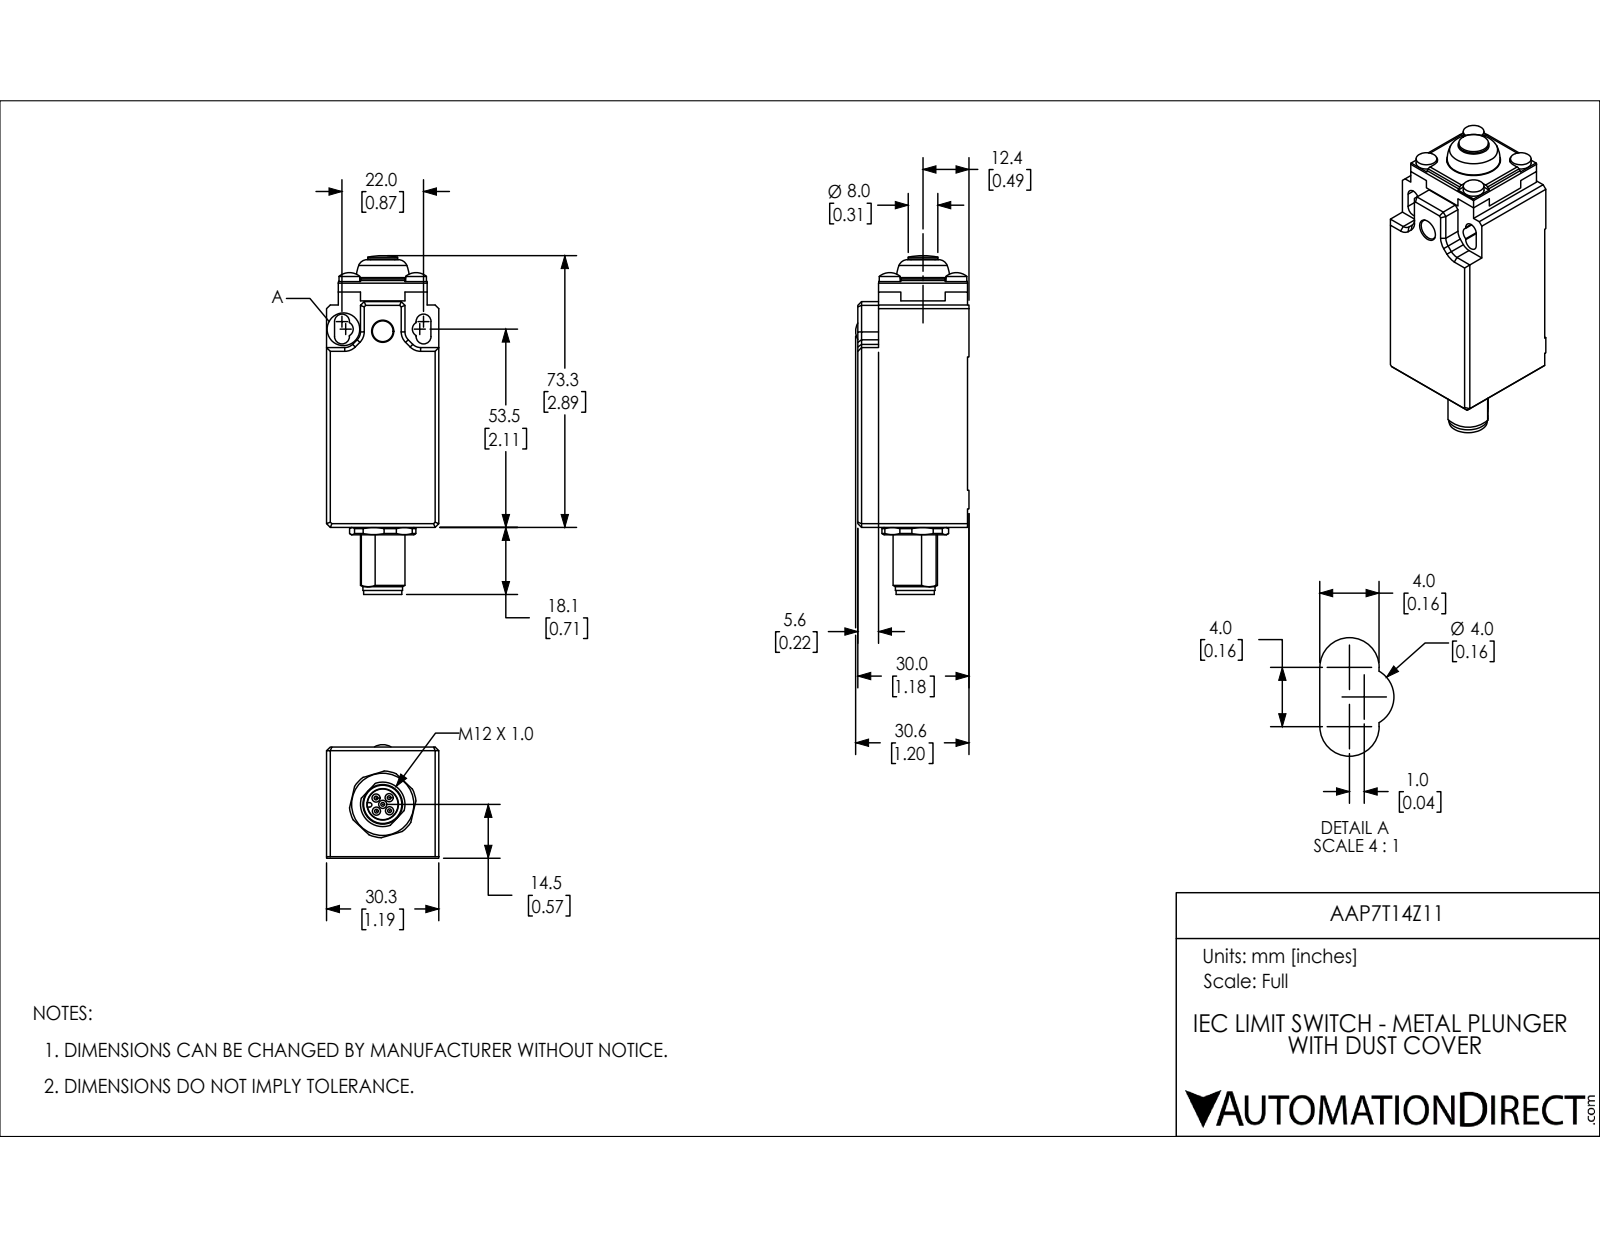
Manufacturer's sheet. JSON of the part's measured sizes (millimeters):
{"part_name": "AAP7T14Z11", "step_written_by": "SolidWorks 2018 (AUTOMOTIVE_DESIGN)", "units": "millimeters", "bodies": {"solids": 5, "faces": 314, "planar": 139, "cylindrical": 120, "other": 55}, "overall_size": [91.4, 30.6, 30.3], "volume_mm3": 58800, "surface_area_mm2": 15700, "round_holes": [[2.2, 5], [6, 1], [8.1, 1], [13, 1], [14, 1], [14.5, 1], [16, 1]], "round_bosses_or_shafts": [[5.6, 5], [1.4, 5], [1, 5], [14.3, 1], [10.7, 1], [10.3, 1], [8, 1], [6.5, 1]], "partial_cylinders_radius": [[1, 8], [3, 8], [2, 6], [0.6, 1], [6, 1], [9, 1], [10, 1], [10.2, 1]], "face_to_face_distances": [30.3, 29.6, 61.1, 0.4, 30, 6, 24, 1, 1.1, 66.2], "hole_center_spacings": [2.5, 3.5, 1.8, 1.9, 2.1, 3.5, 4.2, 4.3]}
